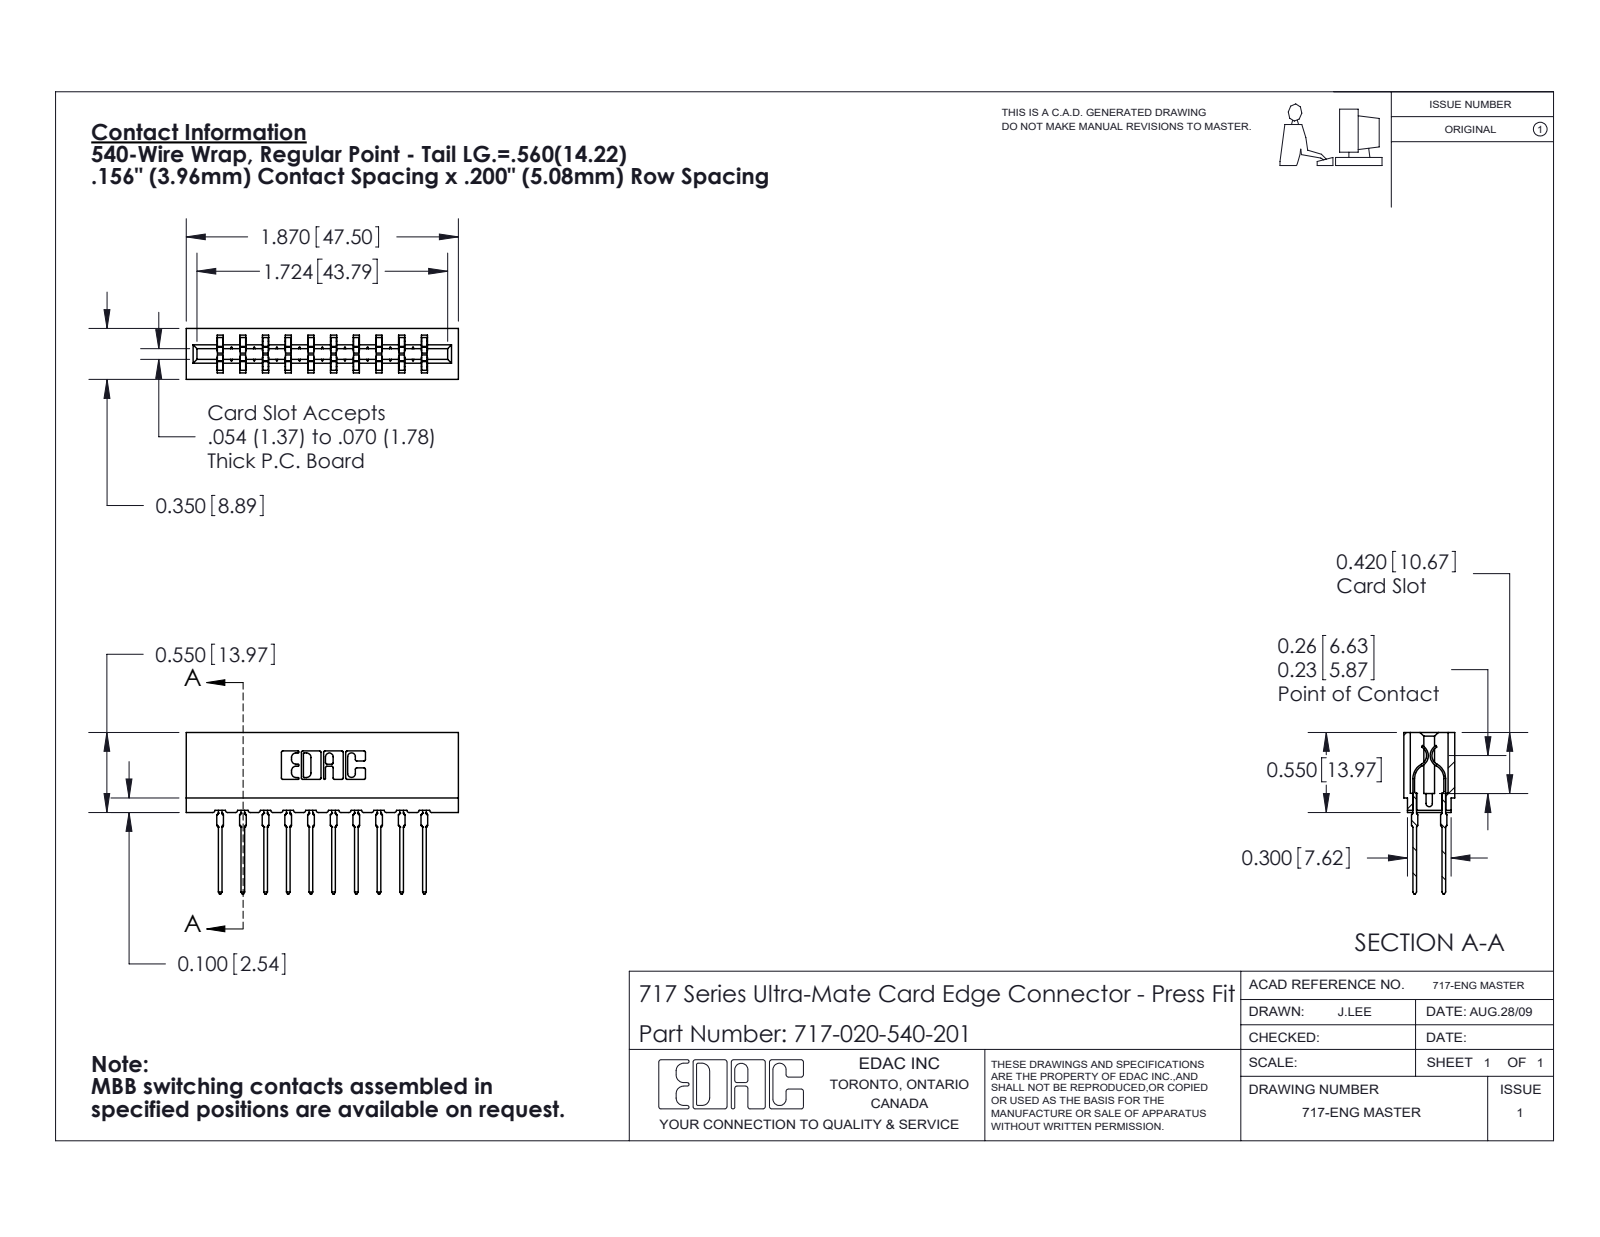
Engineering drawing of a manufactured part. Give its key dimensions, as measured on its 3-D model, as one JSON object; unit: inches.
{"part_name": "717 Part_Insulator Option - 06; 745-292-001_540; 717-020-540-201", "step_written_by": "SolidWorks 2020 (CONFIG_CONTROL_DESIGN)", "units": "inches", "bodies": {"solids": 21, "faces": 1894, "planar": 984, "cylindrical": 390, "other": 520}, "overall_size": [1.87, 1.109, 0.35], "volume_in3": 0.263, "surface_area_in2": 9.949, "partial_cylinders_radius": [[0.021, 40], [0.01, 22], [0.015, 20], [0.005, 8], [0.011, 8], [0.007, 6], [0.031, 6], [0.026, 3]], "face_to_face_distances": [0.156, 0.212, 0.138, 0.624, 0.35, 0.468, 0.198, 0.312, 0.063, 0.287]}
